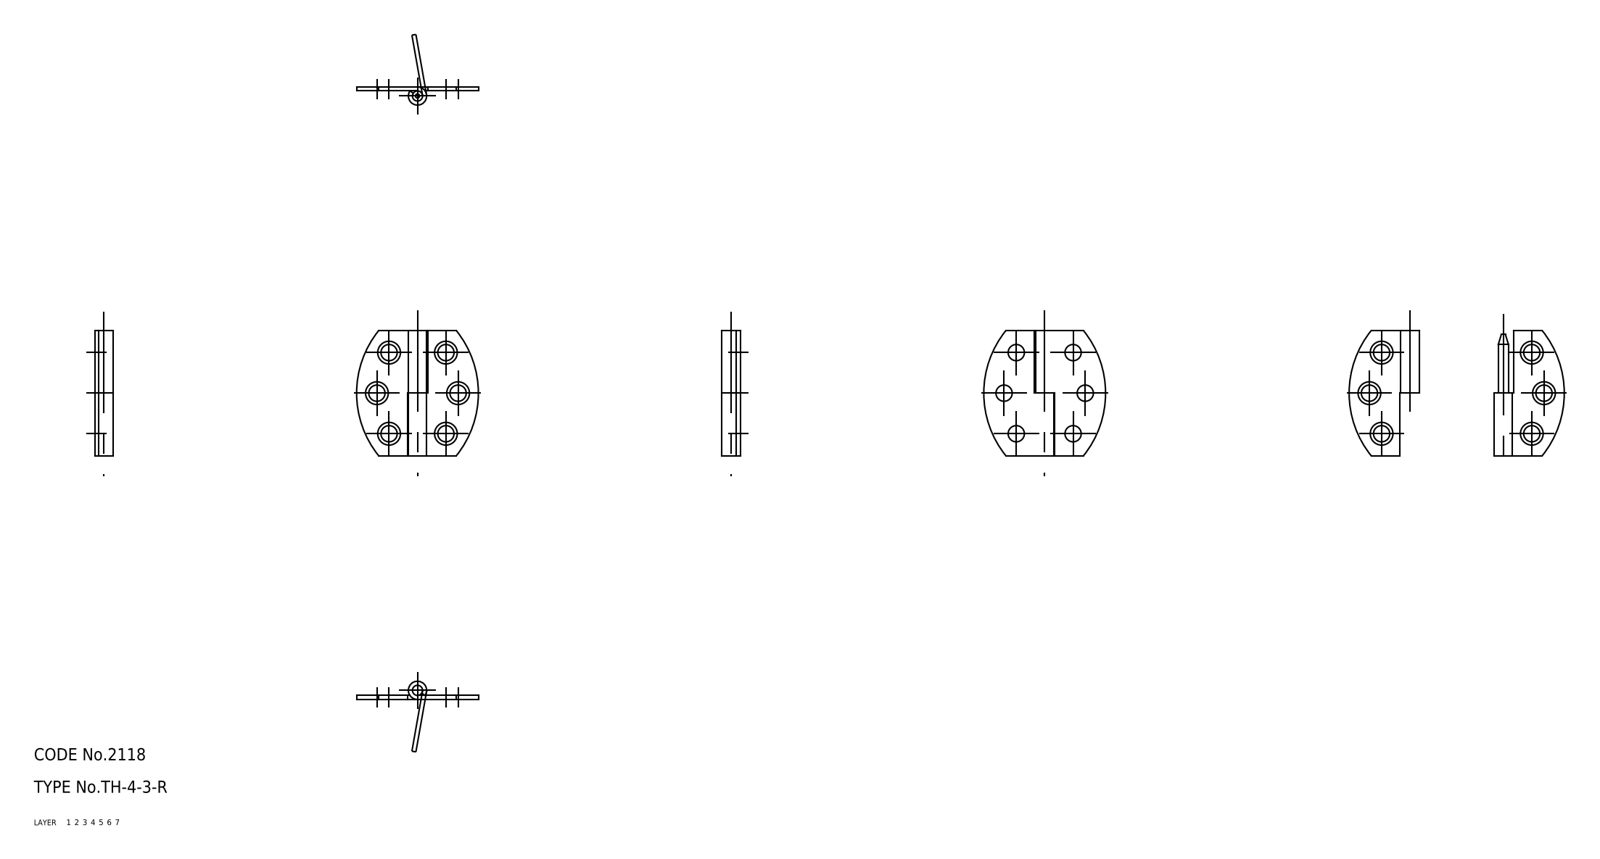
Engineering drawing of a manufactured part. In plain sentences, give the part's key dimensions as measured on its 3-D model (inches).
The part is named "sahft; hinge piece_B; hinge piece_A; TH_4_3_R_9313_36". Its 3-D file was written by "CADfix (AUTOMOTIVE_DESIGN)". It is 3 solids with 50 faces: 0 planar, 0 cylindrical and 50 other. Overall it measures 1.22 by 1.181 by 0.177 inches. Its volume is 0.065 cubic inches and its surface area 3.714 square inches.
